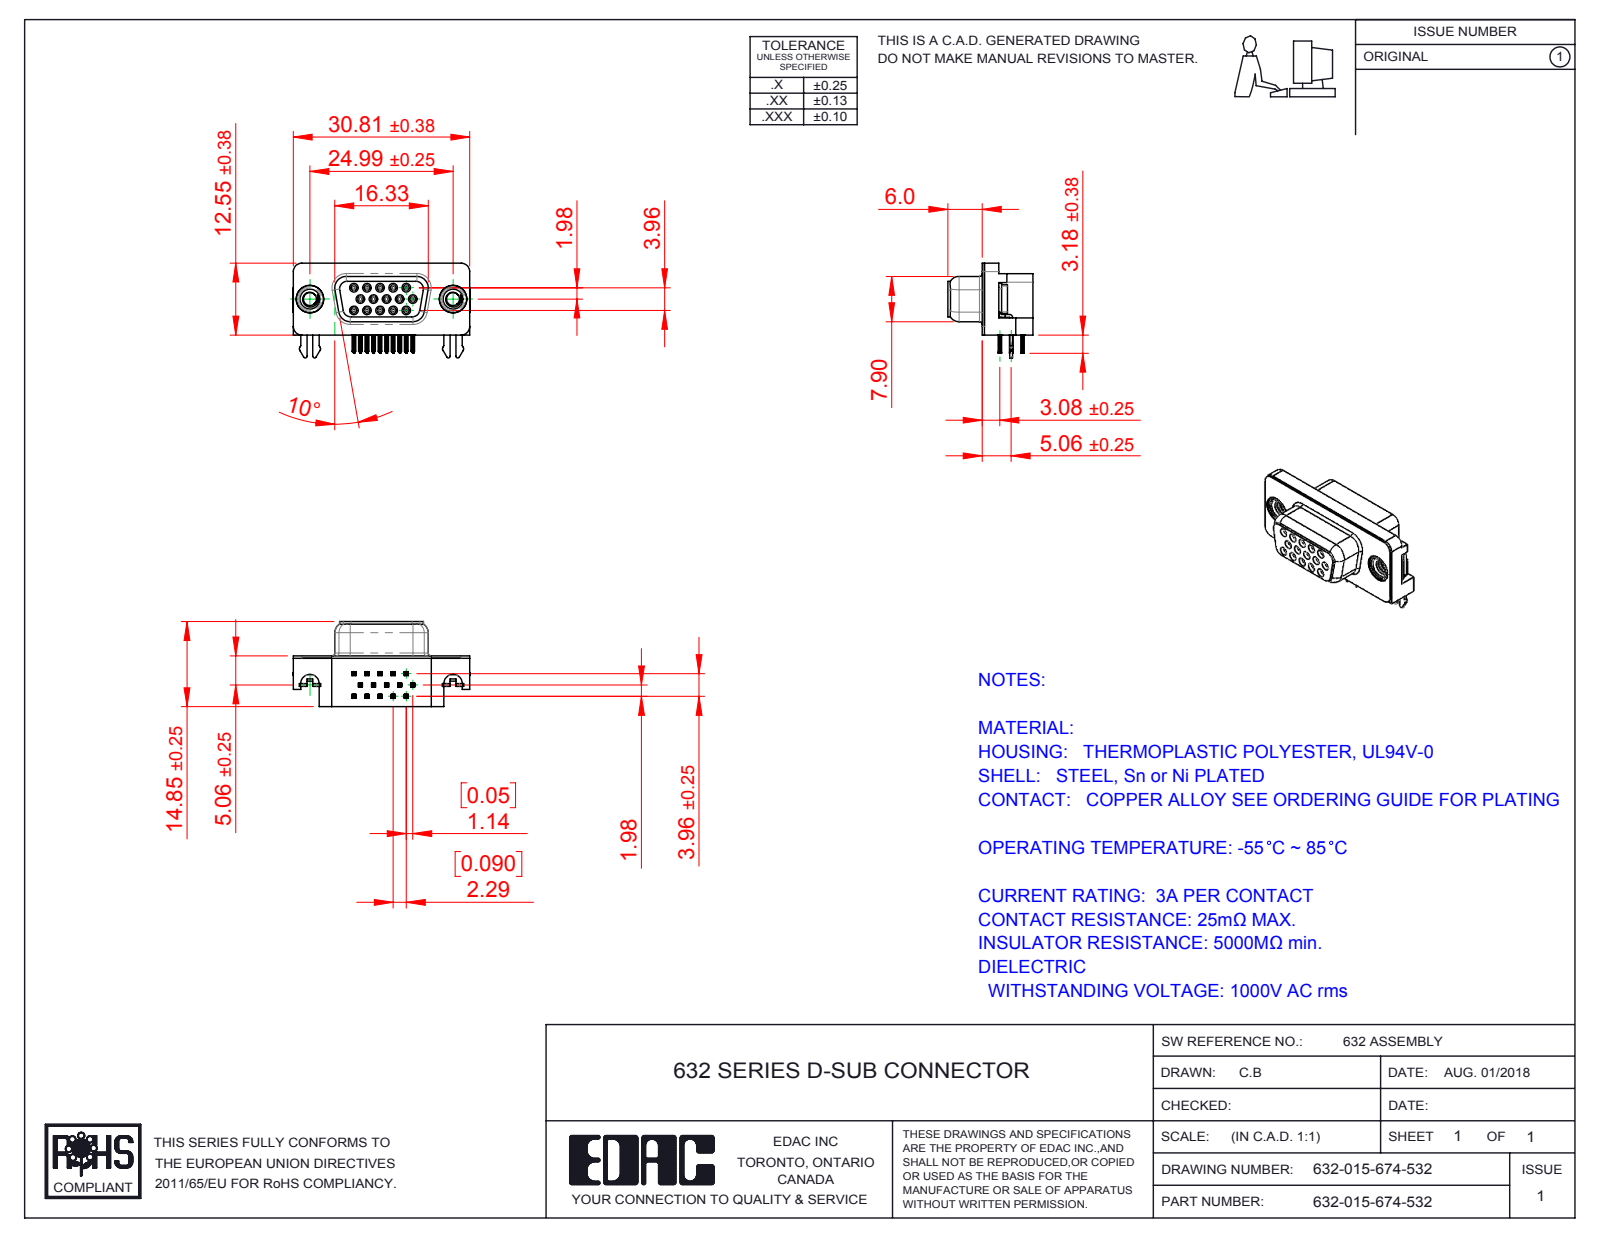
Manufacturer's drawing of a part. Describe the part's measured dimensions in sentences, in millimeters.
The part is named "632 Housing_15 Socket; 632 Shell_9 Socket; 632-015-674-502; 632 Contact Middle_Recessed (+5 more)". Its 3-D file was written by "SolidWorks 2016 (CONFIG_CONTROL_DESIGN)". It is 21 solids with 2338 faces: 990 planar, 612 cylindrical and 736 other. Overall it measures 30.89 by 16.55 by 14.85 millimeters. Its volume is 2 921 cubic millimeters and its surface area 5 015 square millimeters. Round holes: 15 of diameter 0.8, 15 of diameter 0.9, 2 of diameter 2.26, 2 of diameter 4, 2 of diameter 4.8, 2 of diameter 5. Round bosses or shafts: 15 of diameter 1.2, 2 of diameter 4.9, 2 of diameter 4.75, 2 of diameter 3.9. Partial cylindrical surfaces (rounded edges, fillets, slot ends): 120 of radius 0.1, 60 of radius 0.15, 30 of radius 0.35, 15 of radius 0.34, 11 of radius 1, 10 of radius 0.28, 10 of radius 0.5, 8 of radius 0.25. The main face-to-face distances are 0.4, 1.98, 8.45, 8.85, 2.9, 2.5, 5.95, 6.4, 6.7, 7.05. The hole center spacings are 2.28, 2.29, 3.96, 4.57, 6.05, 3.97, 4.58, 6.86.
